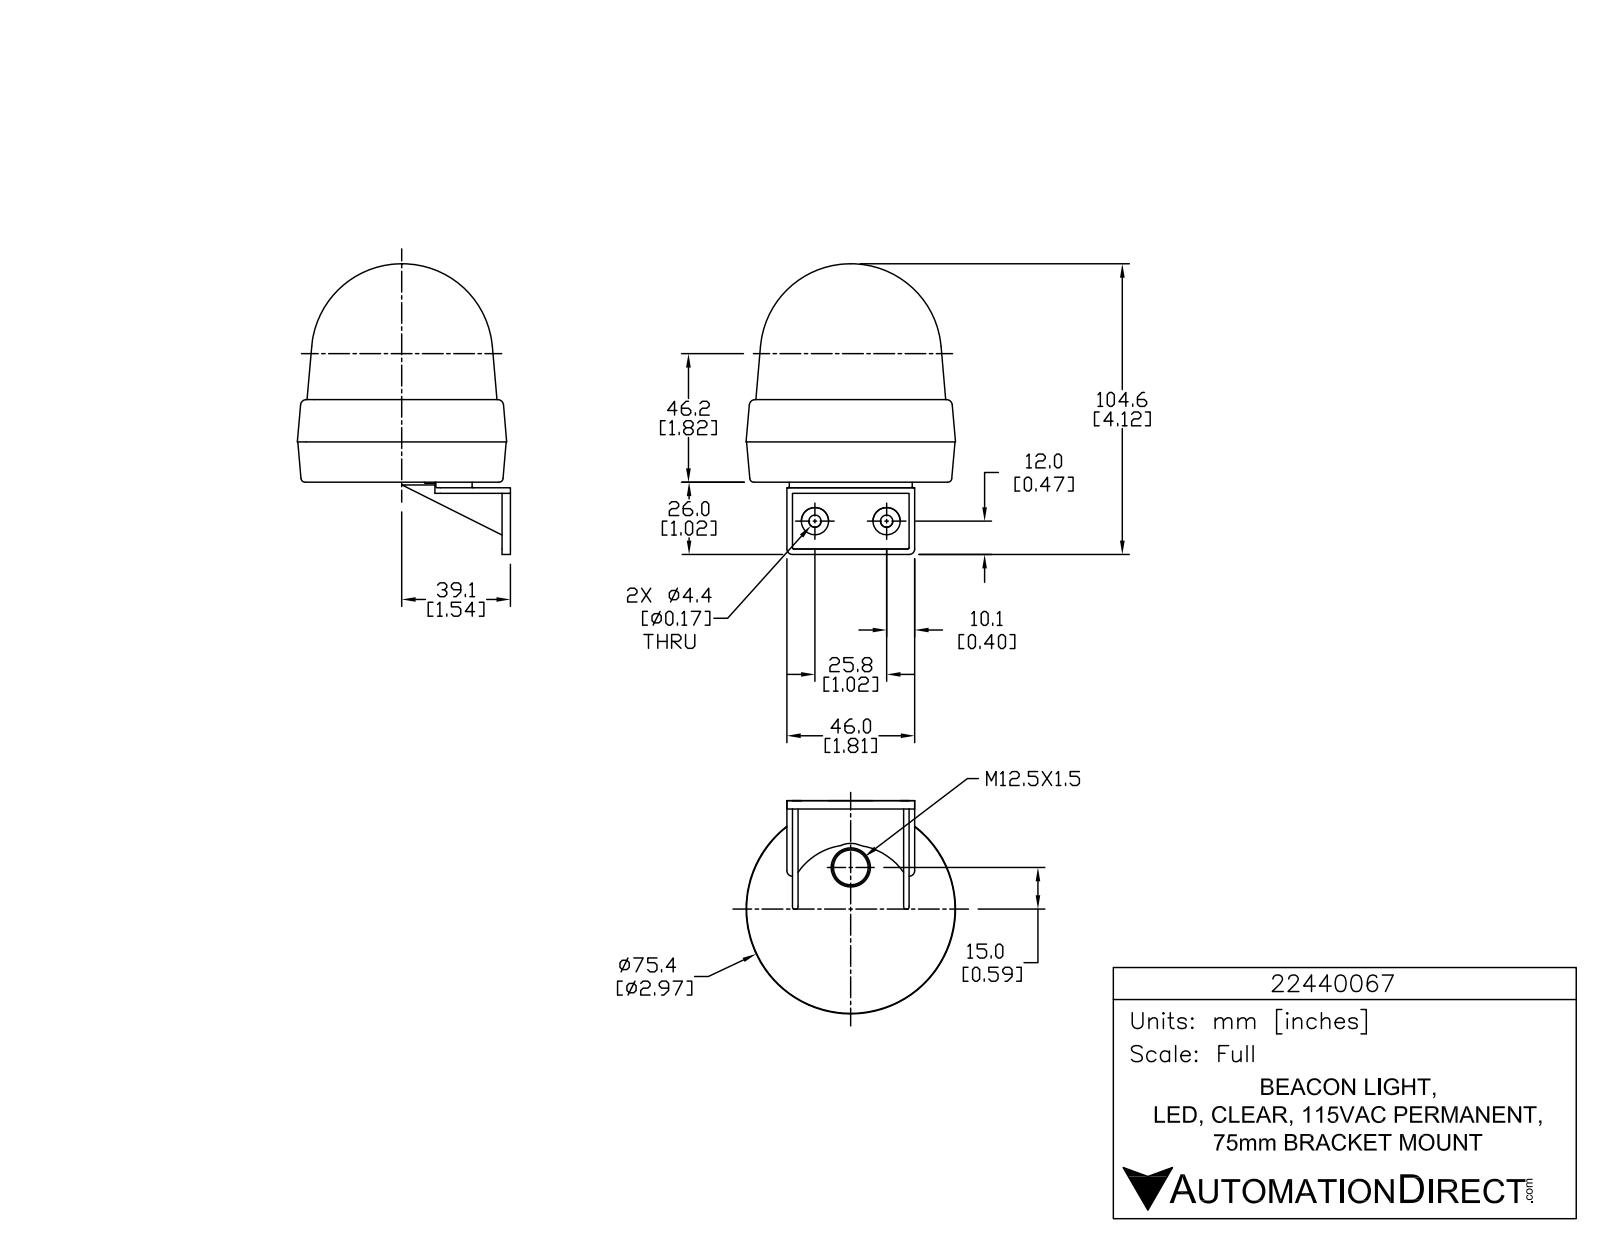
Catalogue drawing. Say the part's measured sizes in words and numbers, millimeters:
The part is named "22440067". Its 3-D file was written by "SolidWorks 2015 (AUTOMOTIVE_DESIGN)". It is 1 solid with 819 faces: 549 planar, 180 cylindrical and 90 other. Overall it measures 104.6 by 82.6 by 75.4 millimeters. Its volume is 262 500 cubic millimeters and its surface area 27 080 square millimeters. Round holes: 3 of diameter 1.5, 2 of diameter 4.4. Round bosses or shafts: 3 of diameter 8.6, 3 of diameter 2.1, 2 of diameter 9.8. Partial cylindrical surfaces (rounded edges, fillets, slot ends): 9 of radius 0.1, 6 of radius 0.1, 6 of radius 0.3, 6 of radius 0.3, 6 of radius 0.3, 6 of radius 0.5, 6 of radius 5, 4 of radius 2. The main face-to-face distances are 2, 4, 40, 1, 3, 42, 38, 2, 42, 44. The hole center spacings are 25.8.
